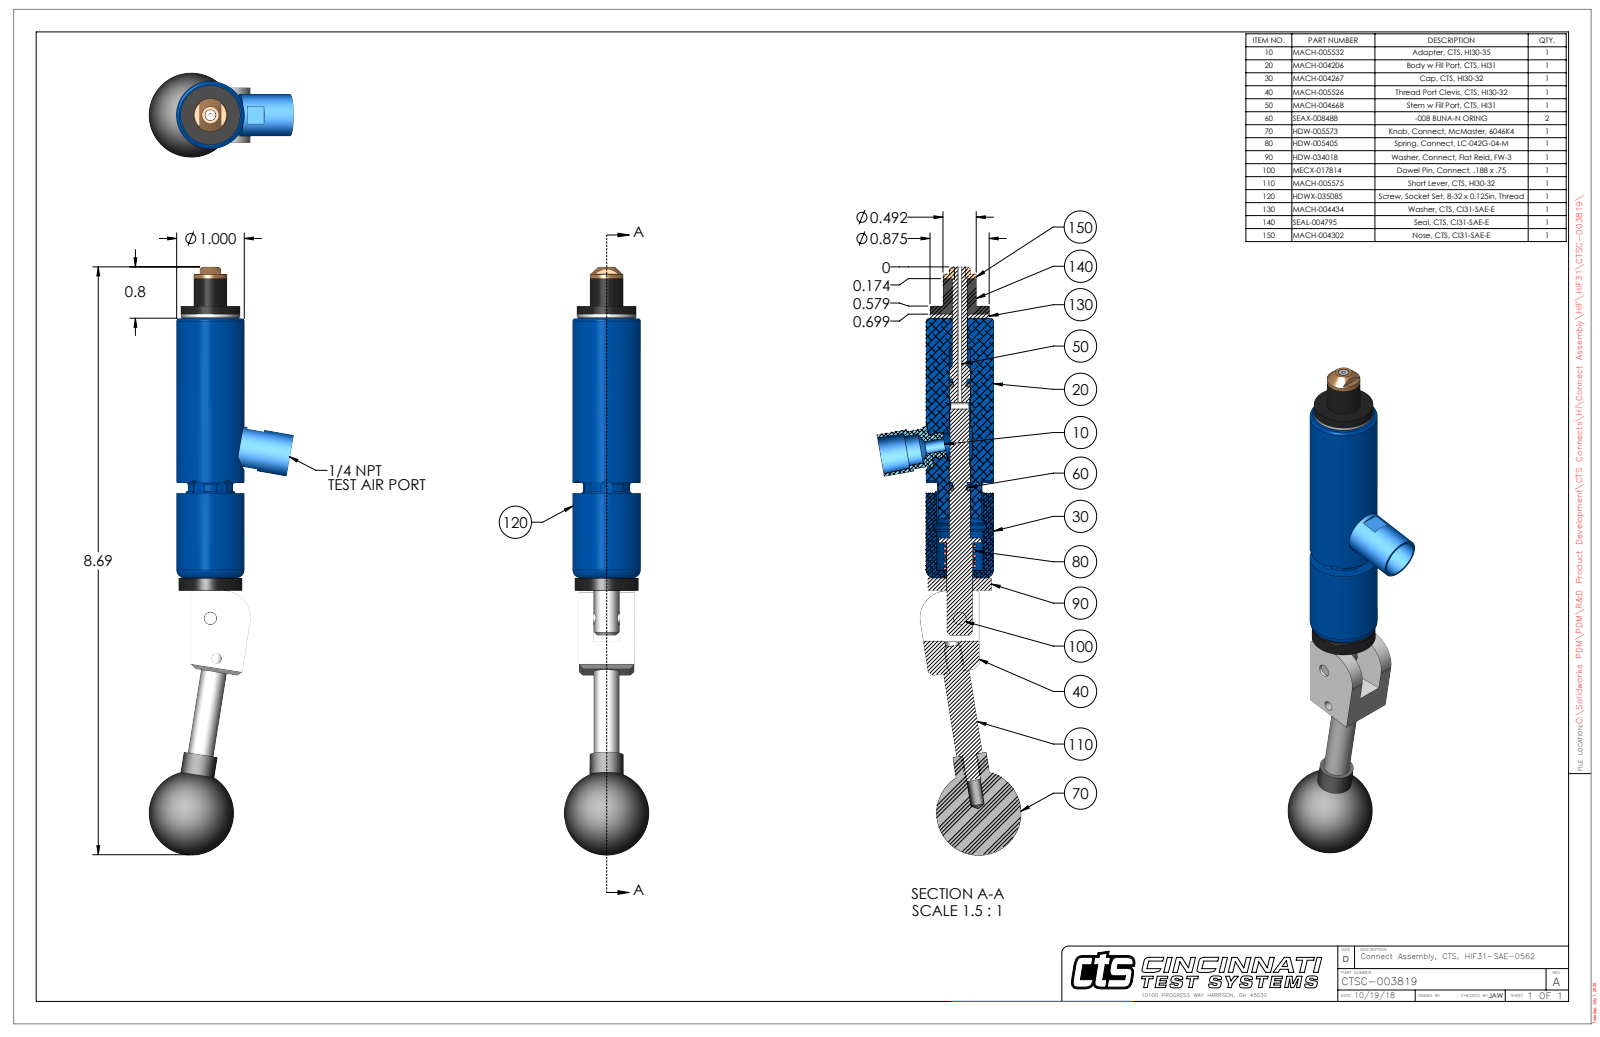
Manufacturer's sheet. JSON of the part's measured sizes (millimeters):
{"part_name": "CTSC-003819", "step_written_by": "SolidWorks 2023 (AUTOMOTIVE_DESIGN)", "units": "millimeters", "bodies": {"solids": 9, "faces": 298, "planar": 113, "cylindrical": 120, "other": 65}, "overall_size": [220.8, 54.1, 31.8], "volume_mm3": 84510, "surface_area_mm2": 26030, "round_holes": [[5.1, 2], [1.6, 1], [2.8, 1], [3.5, 1], [3.8, 1], [4, 1], [4.7, 1], [4.8, 1], [5.5, 1], [5.8, 1], [5.8, 1], [9.8, 1]], "round_bosses_or_shafts": [[25.4, 1], [23.8, 1], [22.2, 1], [22.2, 1], [15.7, 1], [12.7, 1], [12.5, 1], [9.7, 1]], "partial_cylinders_radius": [[2.4, 6], [0.7, 2], [1.5, 1], [8.3, 1], [9.5, 1], [10.2, 1], [11.8, 1]], "face_to_face_distances": [5.3, 15.3, 1.5, 99, 97.4, 20.6, 103.7, 102.2, 4.7, 9.9], "hole_center_spacings": [15.2, 42.1, 57.2]}
